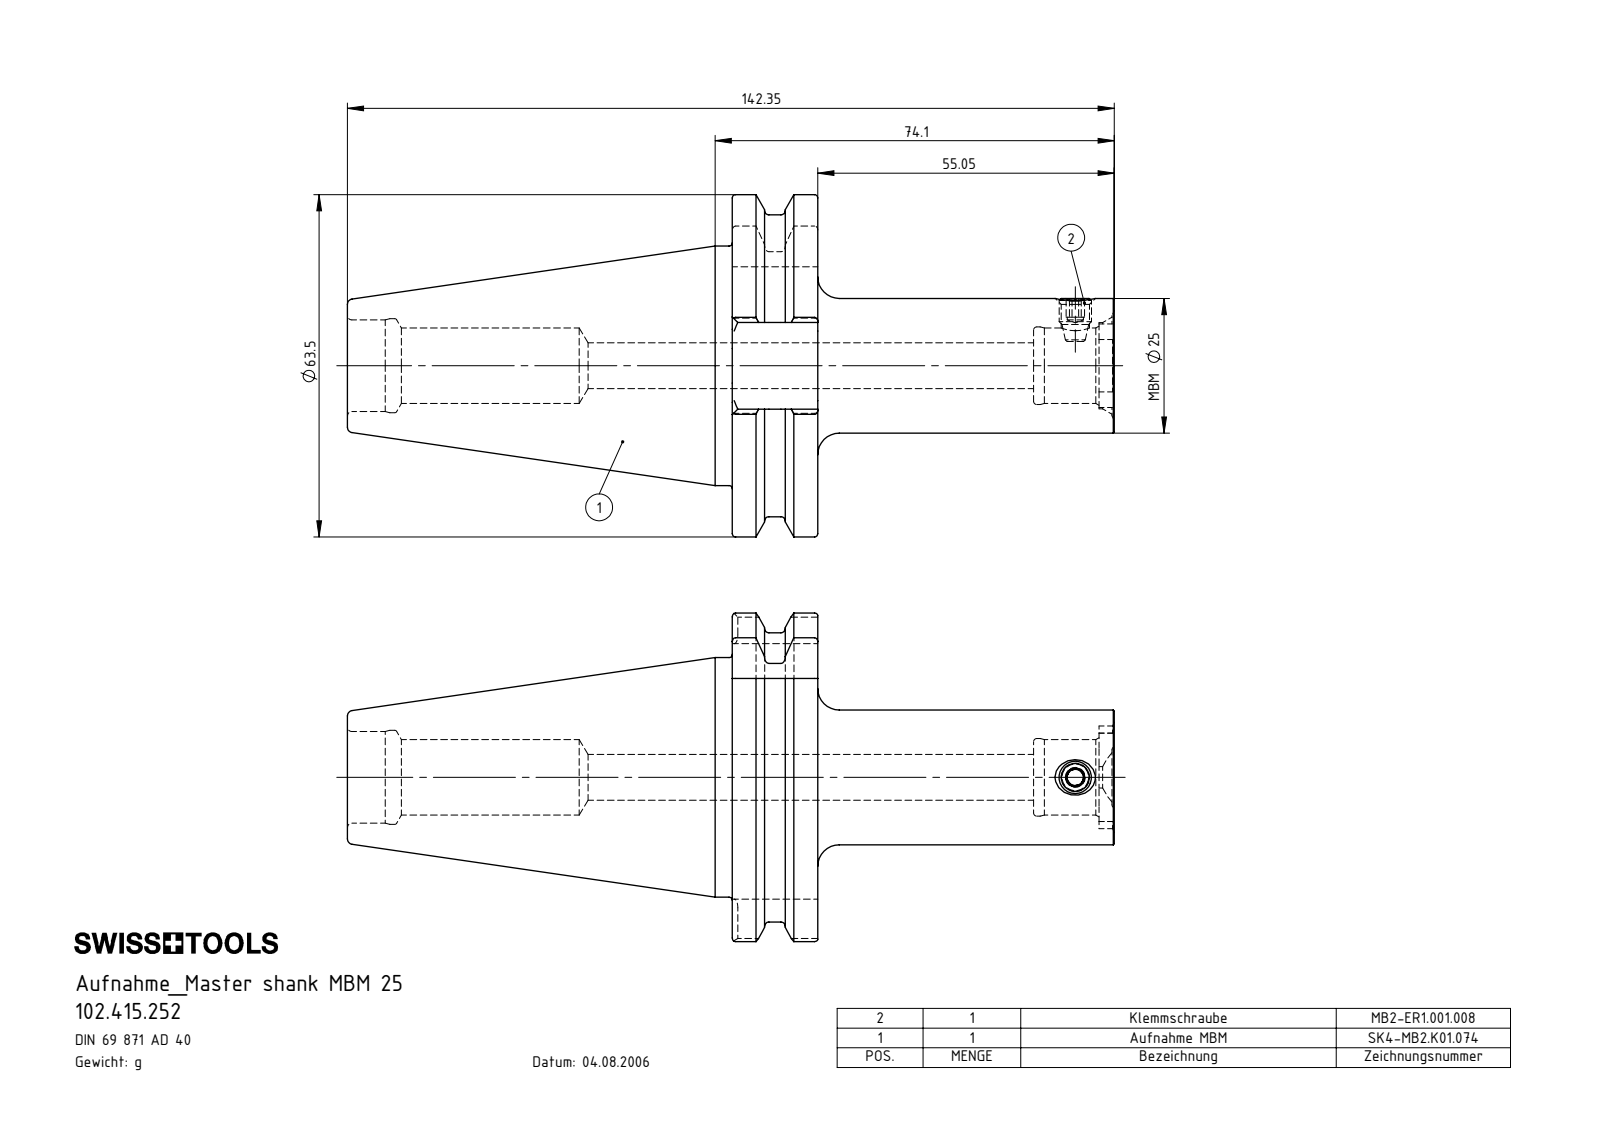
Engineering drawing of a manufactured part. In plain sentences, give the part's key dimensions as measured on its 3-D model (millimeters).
The part is named "MB2-ER1.001.008_A; SK4-MB2.K01.074_C; 102.415.252". Its 3-D file was written by "SolidWorks 2017 (CONFIG_CONTROL_DESIGN)". It is 2 solids with 169 faces: 53 planar, 50 cylindrical and 66 other. Overall it measures 142.35 by 63.5 by 60.94 millimeters. Its volume is 125 956 cubic millimeters and its surface area 25 674 square millimeters. Round holes: 1 of diameter 3, 1 of diameter 5.25, 1 of diameter 8.5, 1 of diameter 14, 1 of diameter 14.4, 1 of diameter 17, 1 of diameter 17.45. Round bosses or shafts: 1 of diameter 44.45, 1 of diameter 25, 1 of diameter 6. Partial cylindrical surfaces (rounded edges, fillets, slot ends): 8 of radius 1.6, 4 of radius 2.7, 1 of radius 8, 1 of radius 9.53, 1 of radius 28, 1 of radius 31.75. The main face-to-face distances are 15.85, 47.4, 70.9, 55.05, 71.45, 87.3, 142.35, 16.1, 139.5, 68.05.
